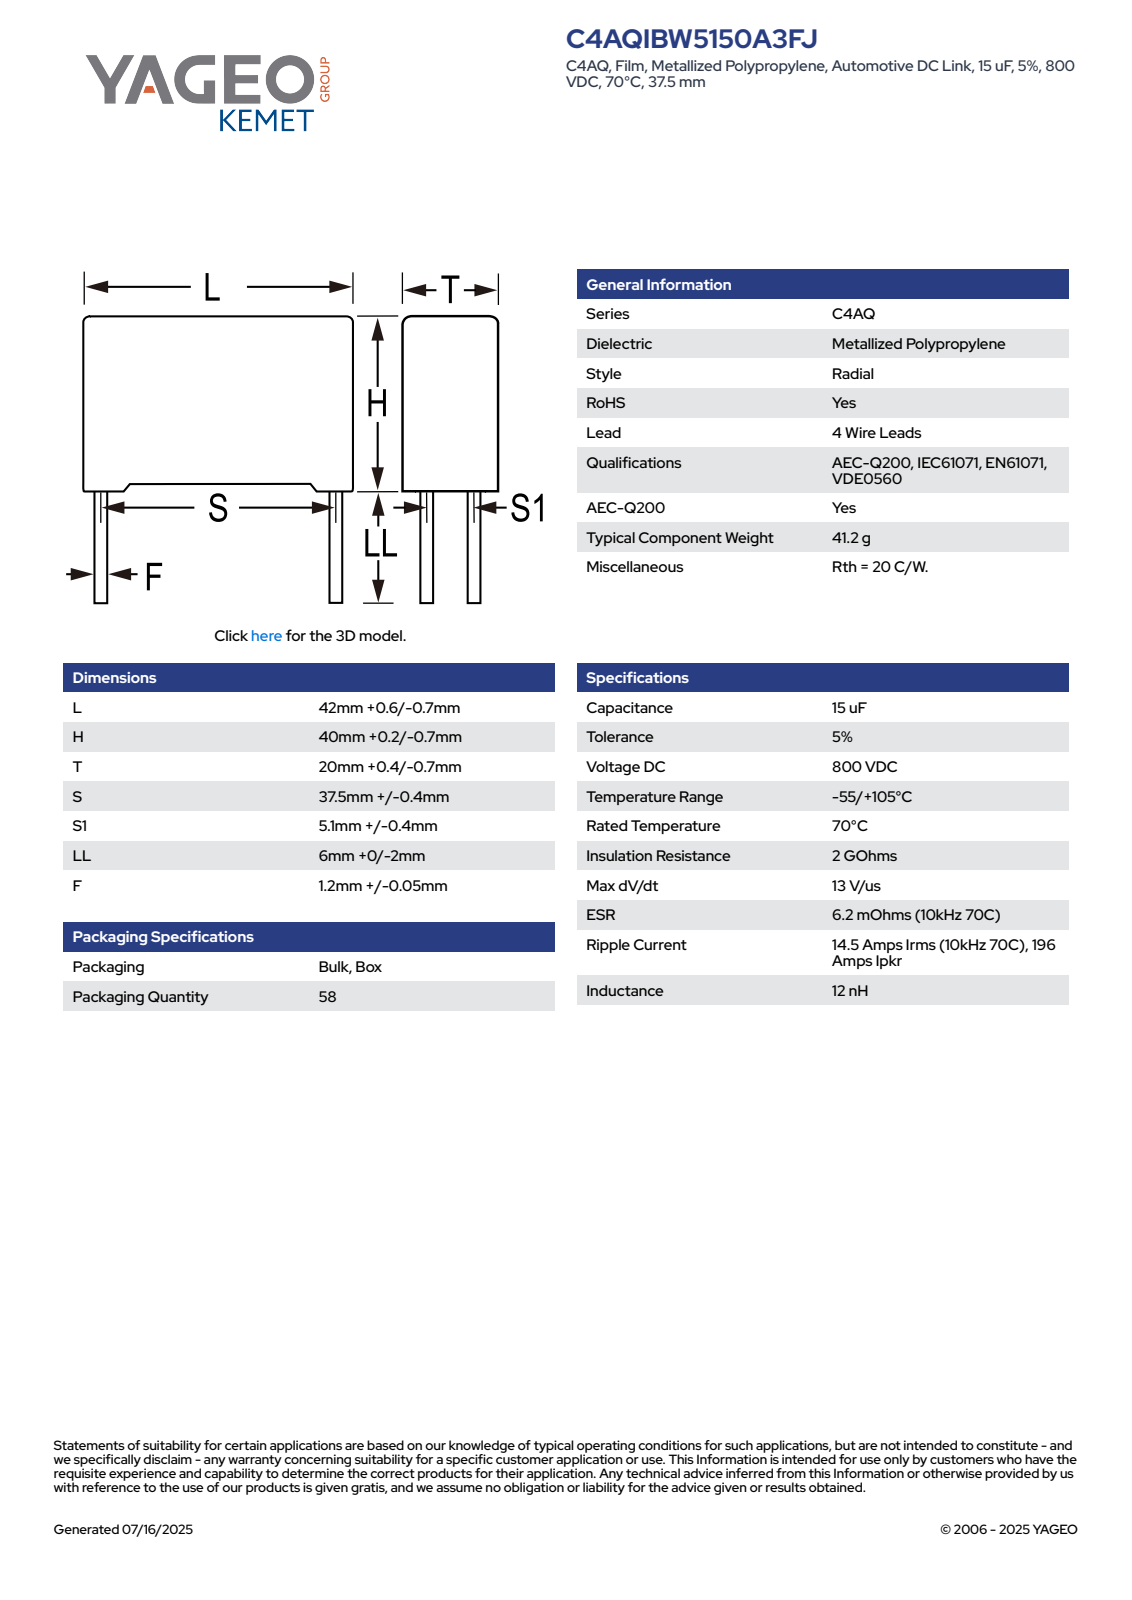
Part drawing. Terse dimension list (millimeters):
name: CFP_RB4_42X40X20_L42.6H40.2T20.4S37.5S15.1LL6F1.25
written by: SolidWorks 2014 (AUTOMOTIVE_DESIGN)
unit: mm
bodies: 4 solids, 87 faces (79 planar, 8 cylindrical, 0 other)
size: 46.2 × 42.6 × 20.41
volume: 34 041 mm³; area: 7 042 mm²
bosses: 4× ⌀1.25
face distances: 20.4, 42.6, 39.02, 1.18, 40.2, 1.25, 20.41, 41.35, 19.15, 40.1
